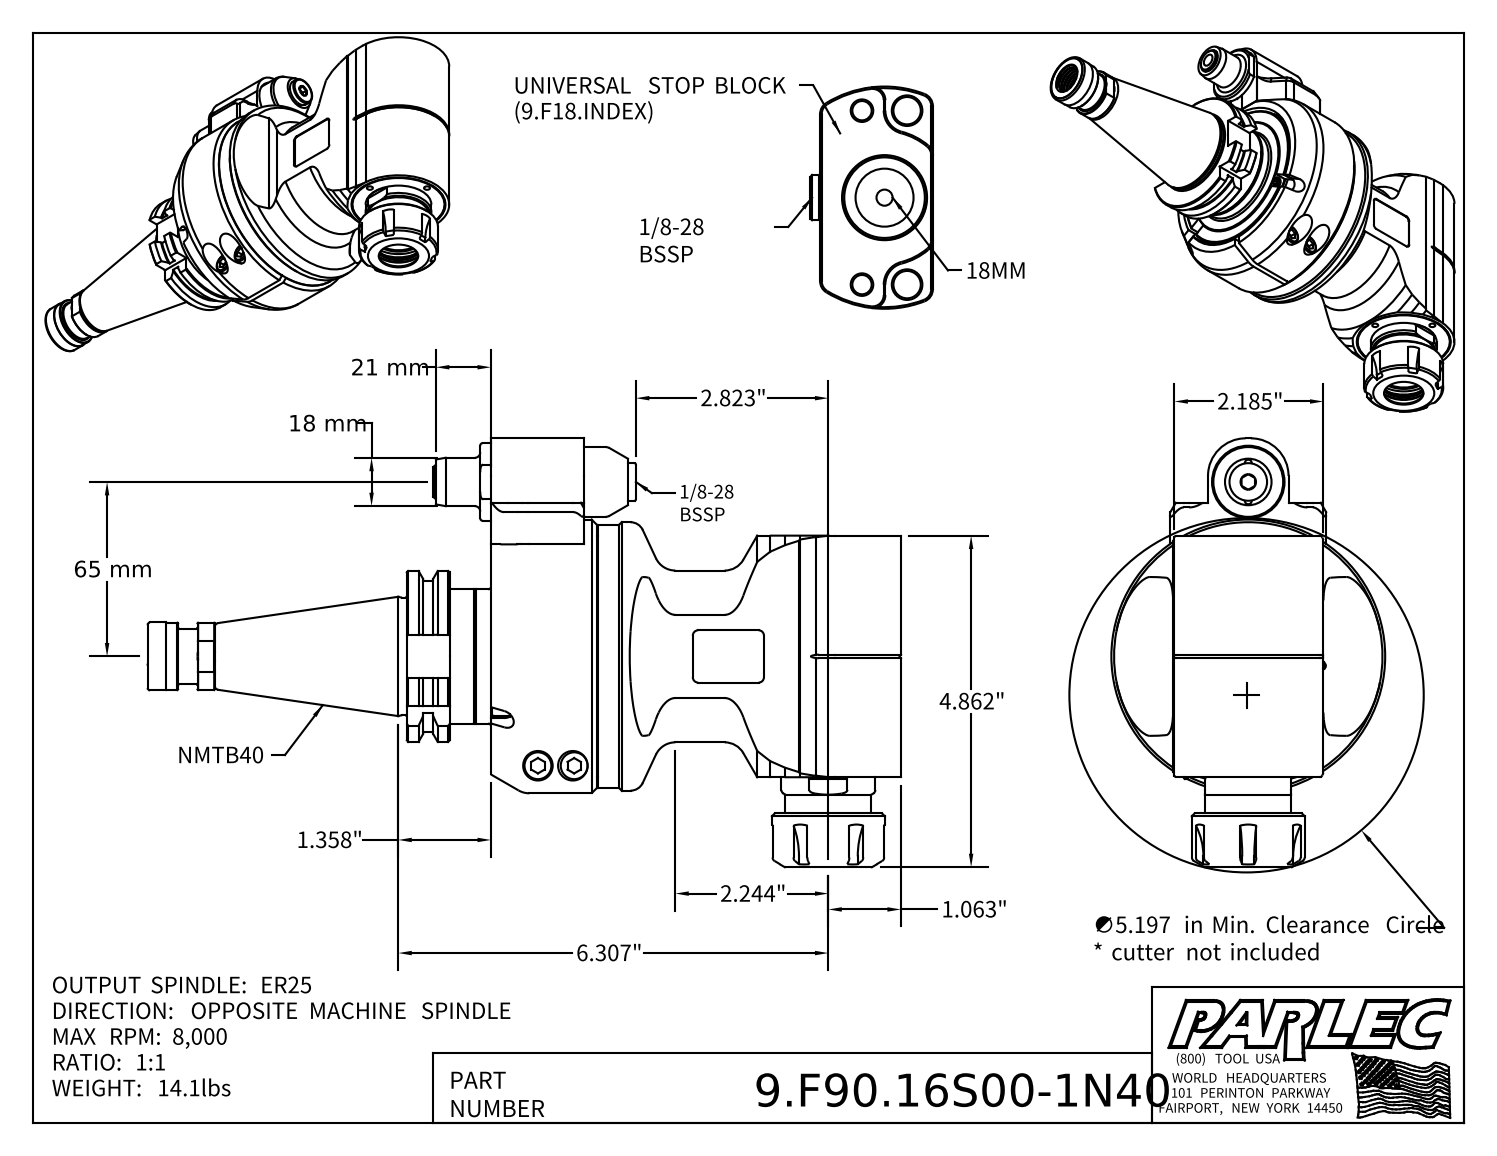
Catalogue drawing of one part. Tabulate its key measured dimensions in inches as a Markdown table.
| quantity | value |
| --- | --- |
| part name | 9.F90.16S00-1N40; 9_GA1_246_2 (Type 1, NMTB40, 65mm); 9_F90_16S00 |
| STEP written by | Autodesk Inventor 2022 (AUTOMOTIVE_DESIGN) |
| units | inches |
| bodies | 6 solids, 630 faces (267 planar, 160 cylindrical, 203 other) |
| overall size | 11.047 × 6.289 × 4.016 |
| volume | 62.03 in³ |
| surface area | 232.6 in² |
| round holes (diameter × count) | 0.126 × 4, 0.102 × 2, 0.165 × 2, 0.197 × 2, 0.276 × 2, 0.409 × 2, 0.433 × 2, 1.063 × 2, 0.098 × 1, 0.118 × 1, 0.256 × 1, 0.335 × 1 |
| round bosses / shafts (diameter × count) | 0.394 × 4, 0.236 × 4, 0.709 × 2, 0.315 × 2, 0.098 × 2, 4.016 × 1, 3.937 × 1, 3.858 × 1 |
| partial cylindrical surfaces (radius × count) | 0.079 × 12, 0.984 × 6, 0.157 × 4, 0.016 × 2, 0.02 × 2, 0.039 × 2, 0.138 × 2, 0.197 × 2 |
| main face-to-face distances | 1.26, 1.252, 0.02, 0.276, 1.535, 1.555, 0.039, 0.295, 0.303, 0.128 |
| hole center spacings | 0.846, 1.197, 0.276, 1.693, 0.512, 0.551, 1.72, 2.283 |
